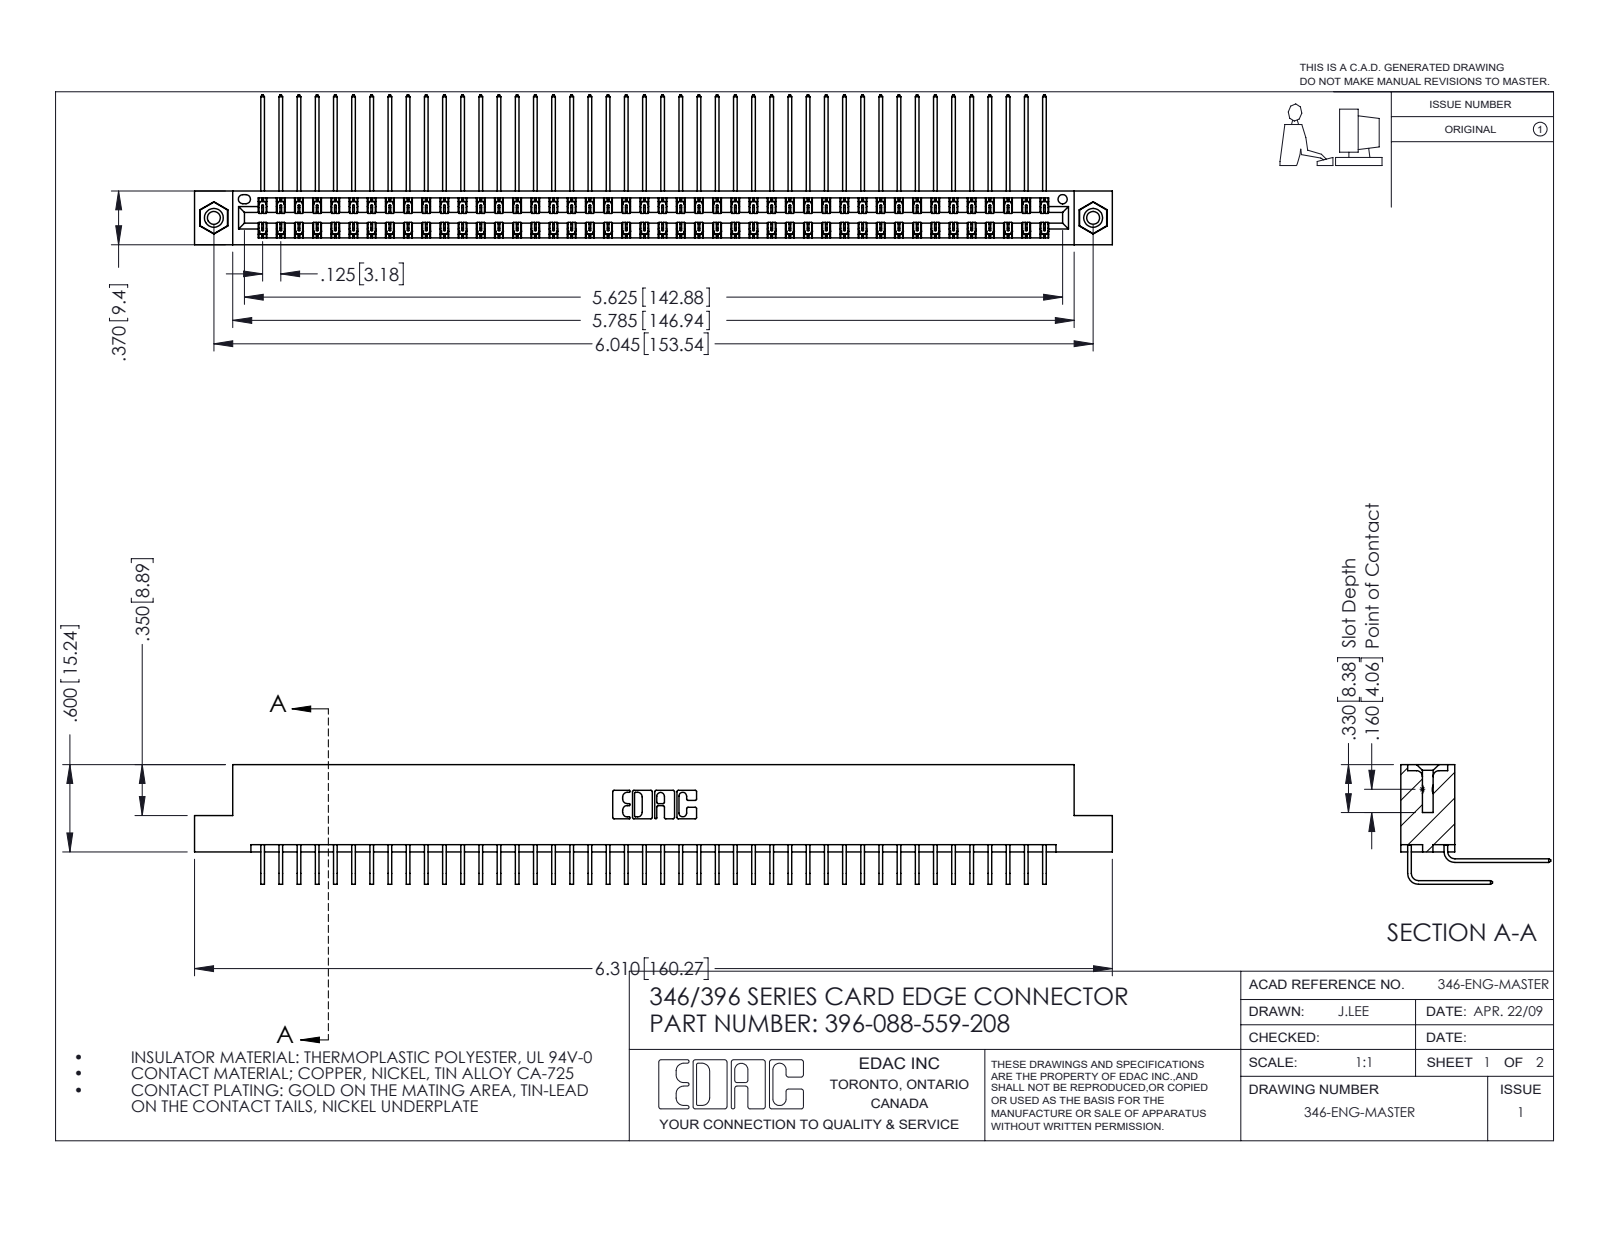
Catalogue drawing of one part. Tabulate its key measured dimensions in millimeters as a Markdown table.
| quantity | value |
| --- | --- |
| part name | 396-088-559-208; 345-292-001_558 559 Tail - 1; 346 Part_Flush Mounting Lugs - 0.156 Dia-TI; 345-250-001_345-250-003-102 (+1 more) |
| STEP written by | SolidWorks 2016 (CONFIG_CONTROL_DESIGN) |
| units | millimeters |
| bodies | 91 solids, 4934 faces (3364 planar, 1554 cylindrical, 16 other) |
| overall size | 160.3 × 26.2 × 20.9 |
| volume | 16 100 mm³ |
| surface area | 24 680 mm² |
| round holes (diameter × count) | 2.3 × 2, 3.2 × 2, 4 × 2, 1.6 × 1 |
| round bosses / shafts (diameter × count) | 3.9 × 2 |
| partial cylindrical surfaces (radius × count) | 0.2 × 132, 0.3 × 22, 0.2 × 6, 0.8 × 6, 0.7 × 3, 0.4 × 2, 0.6 × 2, 0.6 × 2 |
| main face-to-face distances | 1.2, 8.2, 0.6, 9.4, 6.4, 1.8, 7.6, 7, 3.8, 5.6 |
| hole center spacings | 6.2, 148.2, 153.5 |
